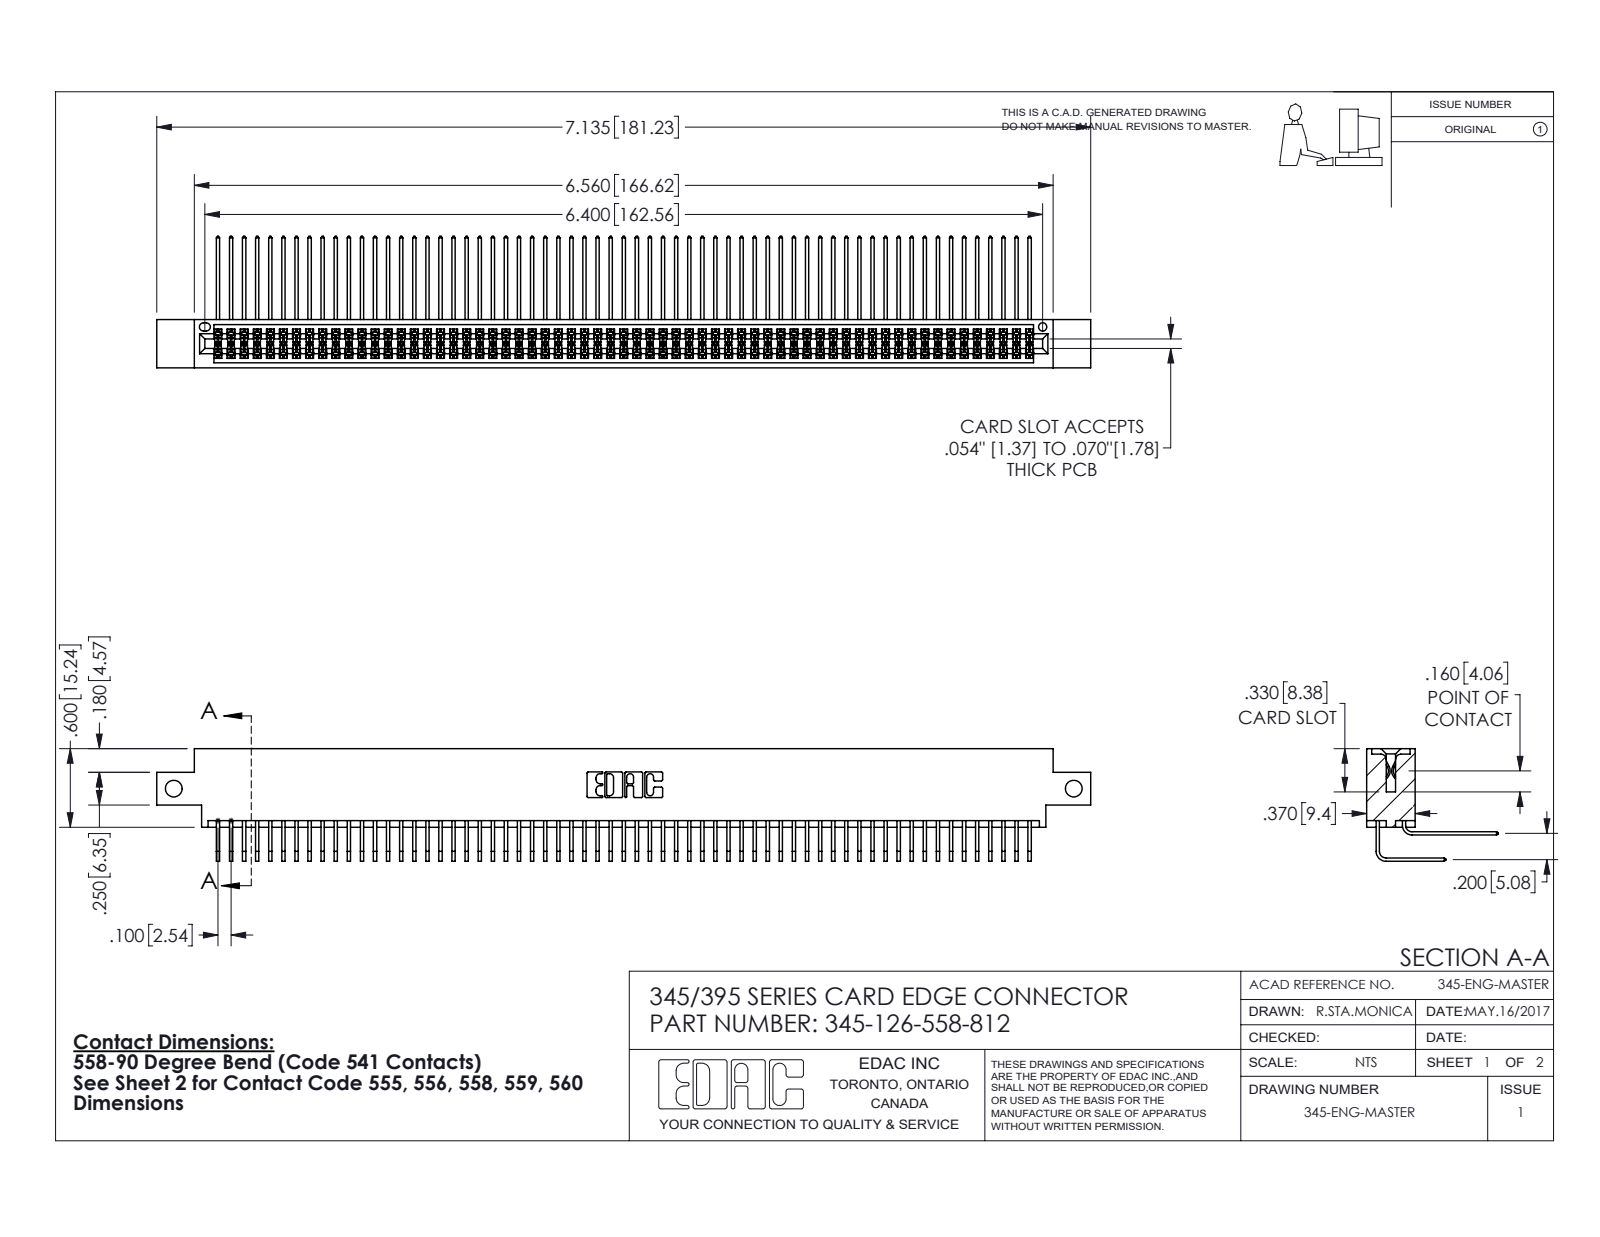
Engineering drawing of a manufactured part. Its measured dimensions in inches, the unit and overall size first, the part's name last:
Units: inches
Overall size (bounding box): 7.135 × 1.005 × 0.859
Round holes (diameter × count): ⌀0.128 ×2, ⌀0.064 ×1
Partial cylindrical surfaces — rounded edges, fillets, slot ends (radius × count): R0.006 ×252, R0.01 ×22, R0.007 ×6, R0.031 ×6, R0.026 ×3, R0.014 ×2, R0.019 ×2, R0.022 ×2
Main face-to-face distances: 0.072, 0.298, 0.2, 0.37, 0.098, 0.272, 0.025, 0.225, 0.175, 0.025
Hole centre spacings: 6.875
Volume: 1.118 in³ · Surface area: 47.93 in²
Bodies: 127 solids, 6682 faces (4494 planar, 2188 cylindrical, 0 other)
Part name (STEP PRODUCT): 345-292-001_558 Tail - 2; 345 Part_0.170 Offset - Side Mount; 345-292-001_558 559 Tail - 1; 345-126-558-812
STEP written by: SolidWorks 2016 (CONFIG_CONTROL_DESIGN)
